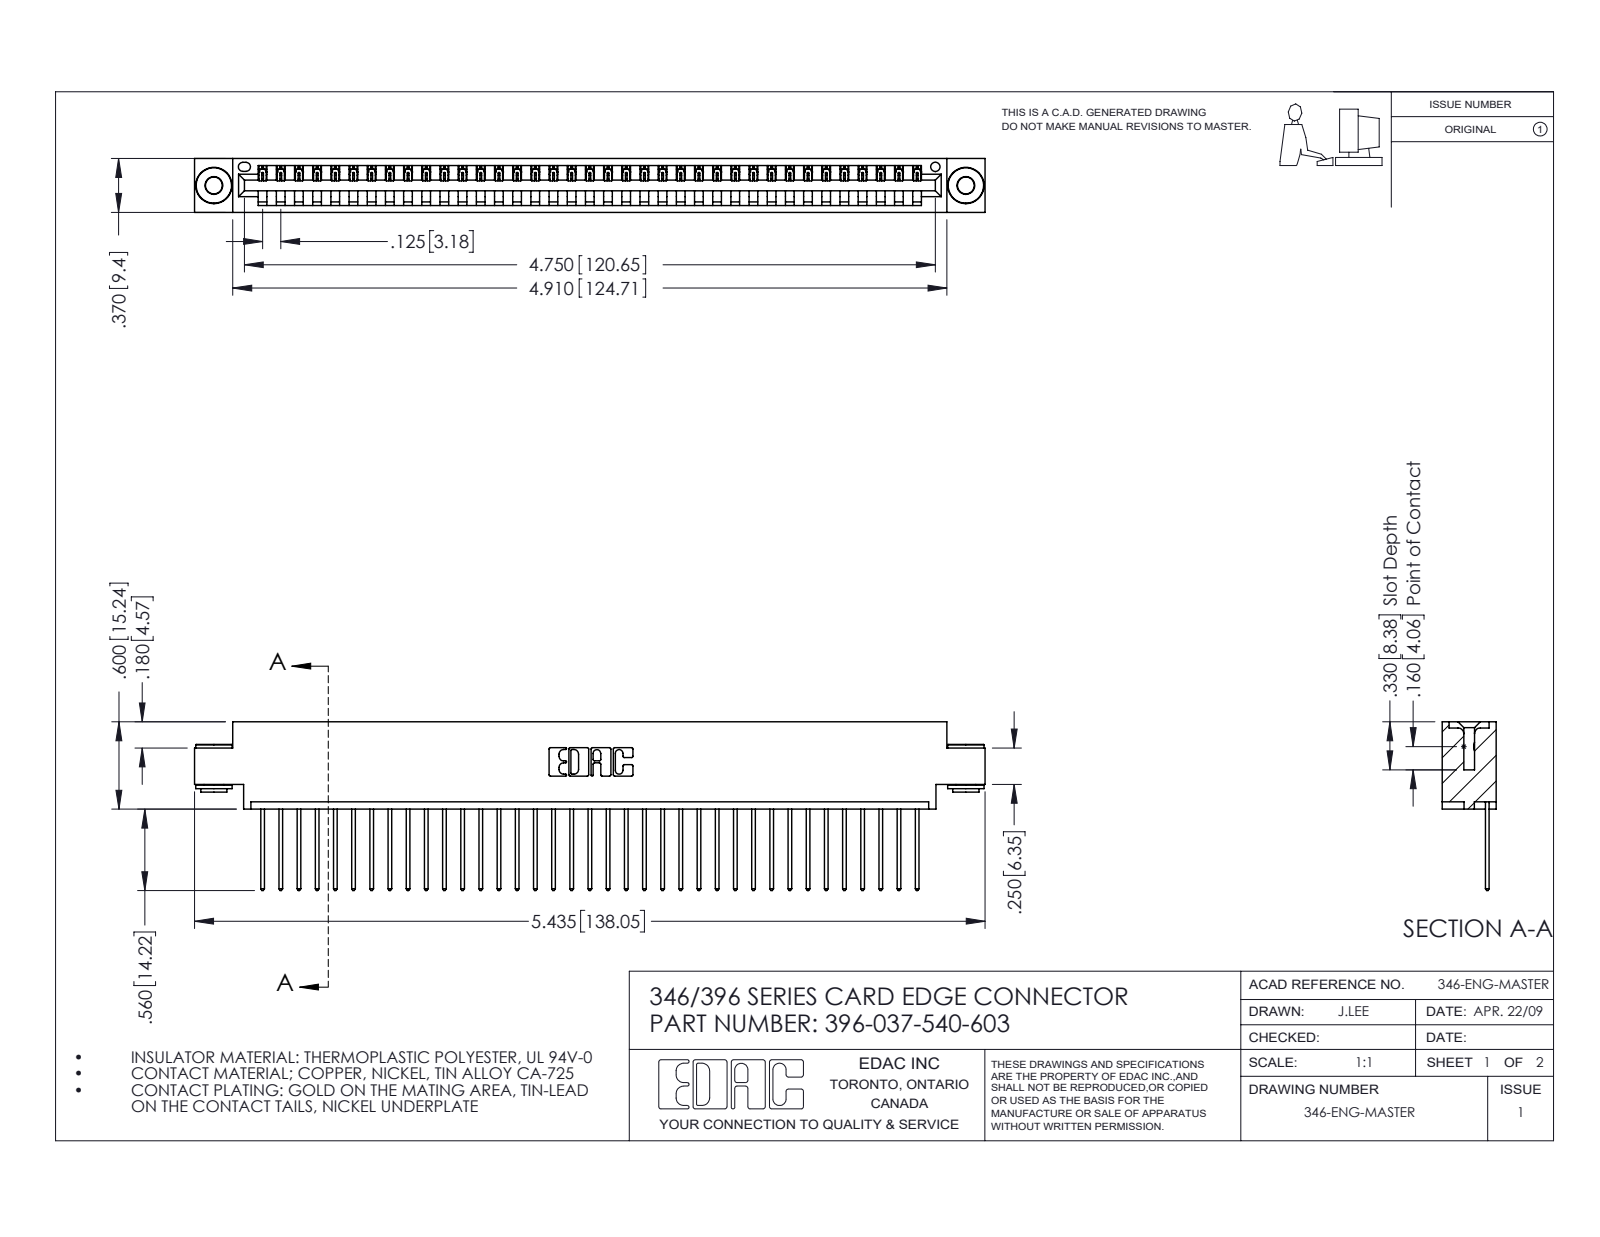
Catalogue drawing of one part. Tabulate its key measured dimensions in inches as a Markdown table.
| quantity | value |
| --- | --- |
| part name | 345-292-001_345-293-140; 346 Part_0.170 Offset - 0.156 Dia-TH; 345-250-002_345-250-002-102; 396-037-540-603 |
| STEP written by | SolidWorks 2016 (CONFIG_CONTROL_DESIGN) |
| units | inches |
| bodies | 40 solids, 2310 faces (1570 planar, 732 cylindrical, 8 other) |
| overall size | 5.435 × 1.16 × 0.37 |
| volume | 0.799 in³ |
| surface area | 26.44 in² |
| round holes (diameter × count) | 0.116 × 2, 0.156 × 2, 0.064 × 1 |
| round bosses / shafts (diameter × count) | 0.25 × 2, 0.18 × 2, 0.136 × 2 |
| partial cylindrical surfaces (radius × count) | 0.006 × 74, 0.01 × 74, 0.01 × 22, 0.007 × 6, 0.031 × 6, 0.026 × 3, 0.031 × 2, 0.04 × 2 |
| main face-to-face distances | 0.048, 0.322, 0.37, 0.25, 0.025, 0.072, 0.298, 0.148, 0.222, 0.1 |
| hole center spacings | 0.246, 4.961, 5.17 |
